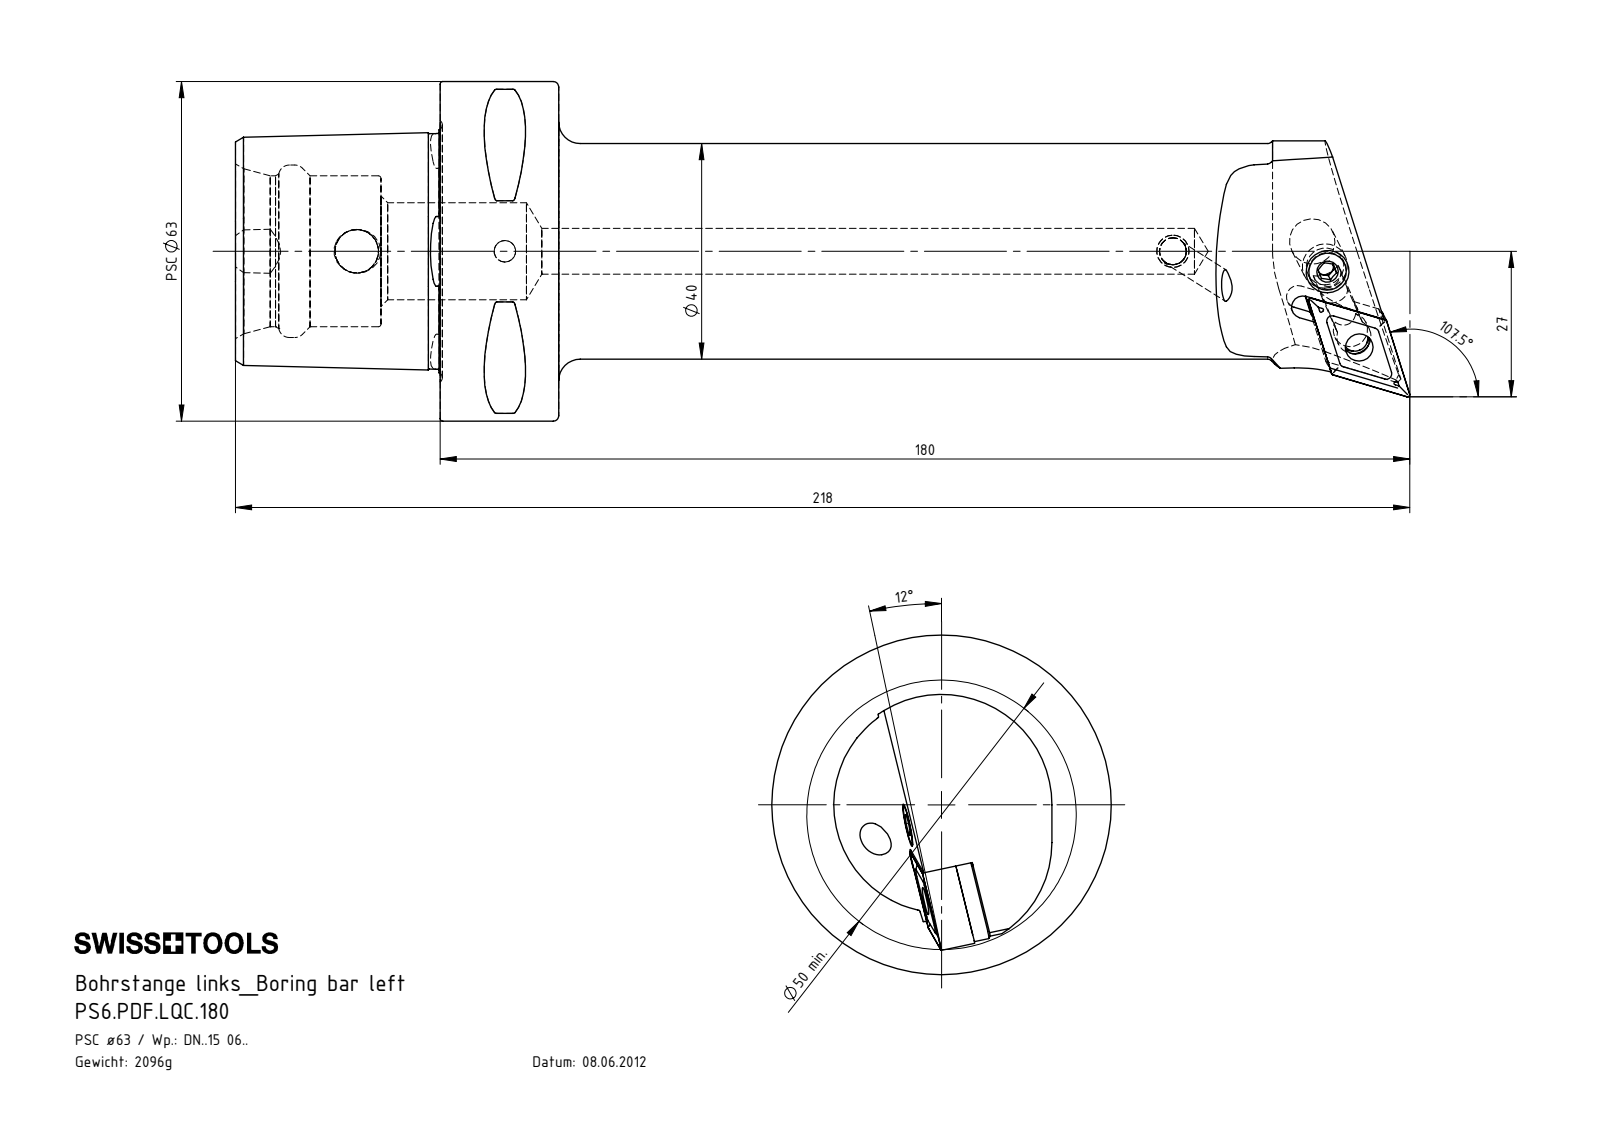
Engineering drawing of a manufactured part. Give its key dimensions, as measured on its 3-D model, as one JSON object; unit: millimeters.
{"part_name": "WCD-ER1.101.000; PS6-PDF.LQC.180_A; WCD-ER4.101.017_A; DNMG150604 (+4 more)", "step_written_by": "SolidWorks 2017 (AUTOMOTIVE_DESIGN)", "units": "millimeters", "bodies": {"solids": 8, "faces": 353, "planar": 92, "cylindrical": 87, "other": 174}, "overall_size": [218, 63, 63], "volume_mm3": 267834, "surface_area_mm2": 46089, "round_holes": [[5, 2], [4, 1], [5.16, 1], [6.4, 1], [7, 1], [8.1, 1], [8.4, 1], [8.5, 1], [18, 1], [28, 1], [32, 1]], "round_bosses_or_shafts": [[63, 1], [40, 1], [8, 1], [7.9, 1], [6.4, 1], [6, 1], [4.7, 1], [3.55, 1]], "partial_cylinders_radius": [[0.5, 8], [0.4, 4], [1, 4], [2.5, 2], [2.1, 1], [2.35, 1], [2.8, 1], [3, 1]], "face_to_face_distances": [22, 38, 60, 6.04, 24.88, 3.18, 9.22, 27, 11, 33], "hole_center_spacings": [15.59, 27.5, 124, 151.5]}
